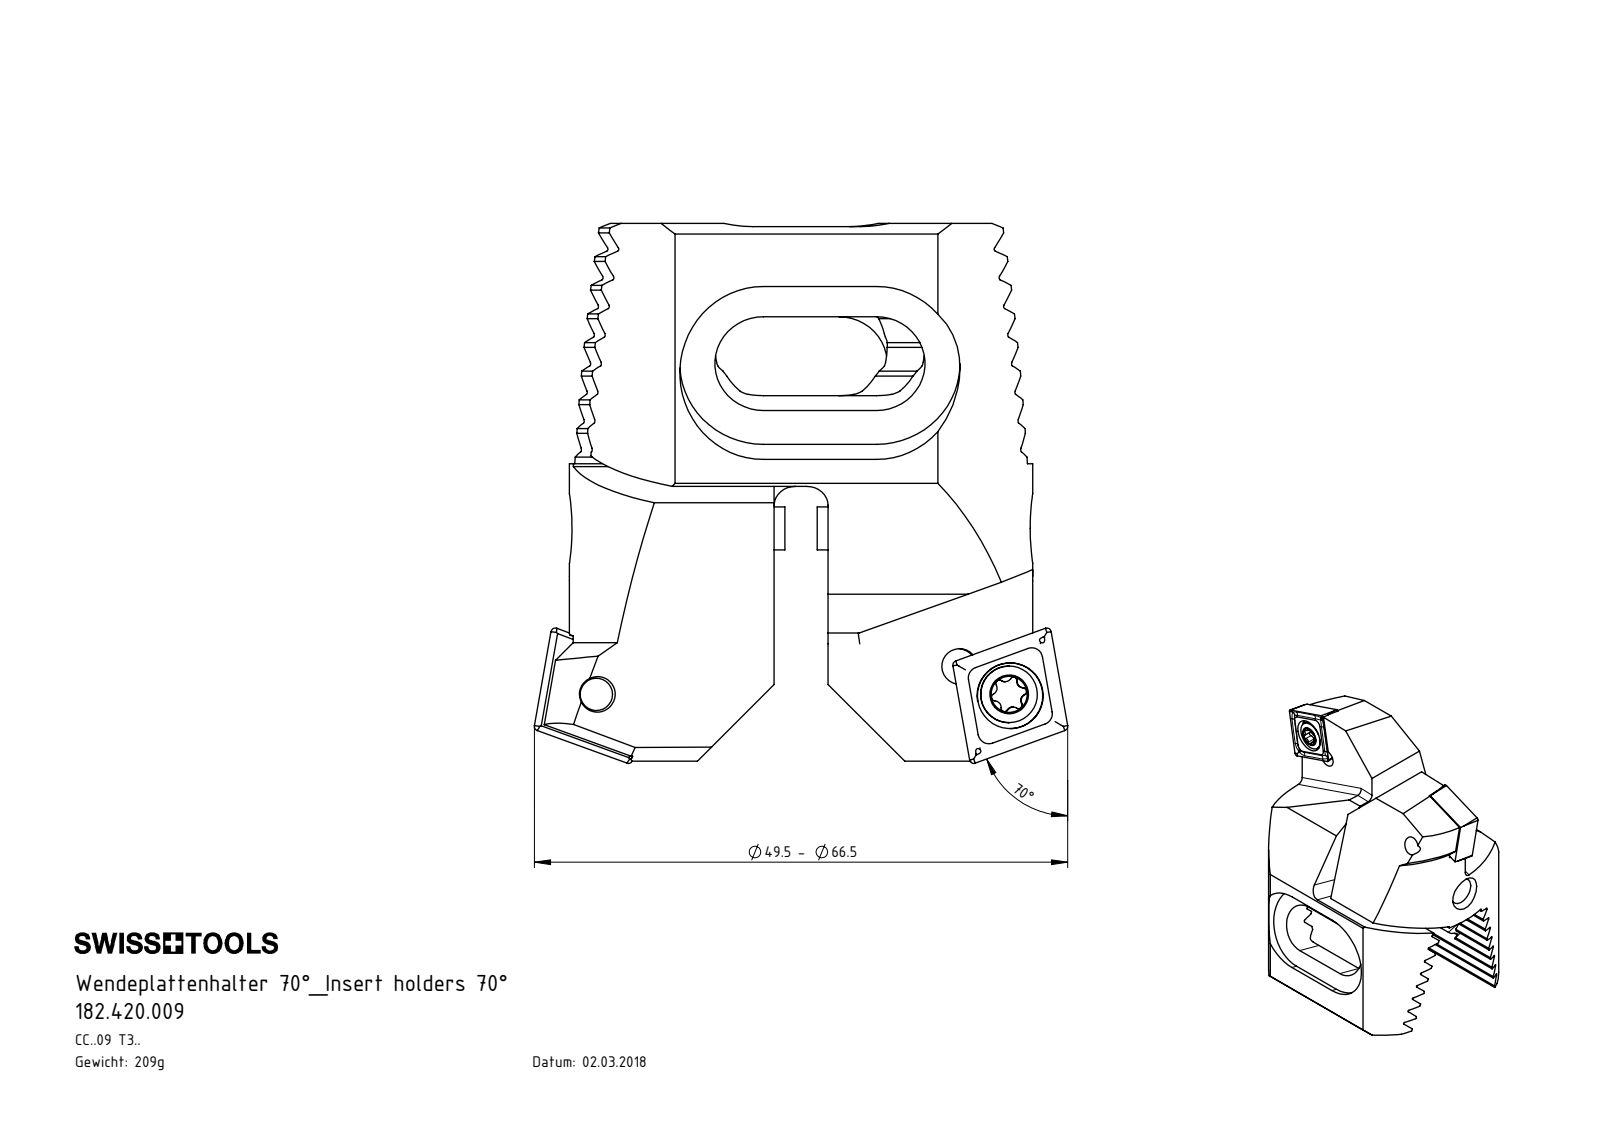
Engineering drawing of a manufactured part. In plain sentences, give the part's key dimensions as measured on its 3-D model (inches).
The part is named "182.420.009; WCB-ER2.001.009_A; CCMT09T304; Z42-ER3.001.016 (+1 more)". Its 3-D file was written by "SolidWorks 2017 (CONFIG_CONTROL_DESIGN)". It is 8 solids with 644 faces: 330 planar, 130 cylindrical and 184 other. Overall it measures 1.972 by 1.949 by 1.346 inches. Its volume is 1.624 cubic inches and its surface area 20.81 square inches. Round holes: 4 of diameter 0.13, 2 of diameter 0.063, 2 of diameter 0.173, 2 of diameter 0.24, 1 of diameter 0.197. Round bosses or shafts: 3 of diameter 0.157, 2 of diameter 0.207, 1 of diameter 0.236. Partial cylindrical surfaces (rounded edges, fillets, slot ends): 16 of radius 0.008, 12 of radius 0.013, 12 of radius 0.023, 4 of radius 0.039, 4 of radius 0.079, 4 of radius 0.177, 4 of radius 0.305, 4 of radius 0.472. The main face-to-face distances are 0.094, 0.187, 0.469, 0.375, 0.563, 0.281, 0.188, 0.281, 0.063, 0.228. The hole center spacings are 0.208, 0.214, 0.472, 1.343, 1.347, 1.524, 0.913, 1.157.
